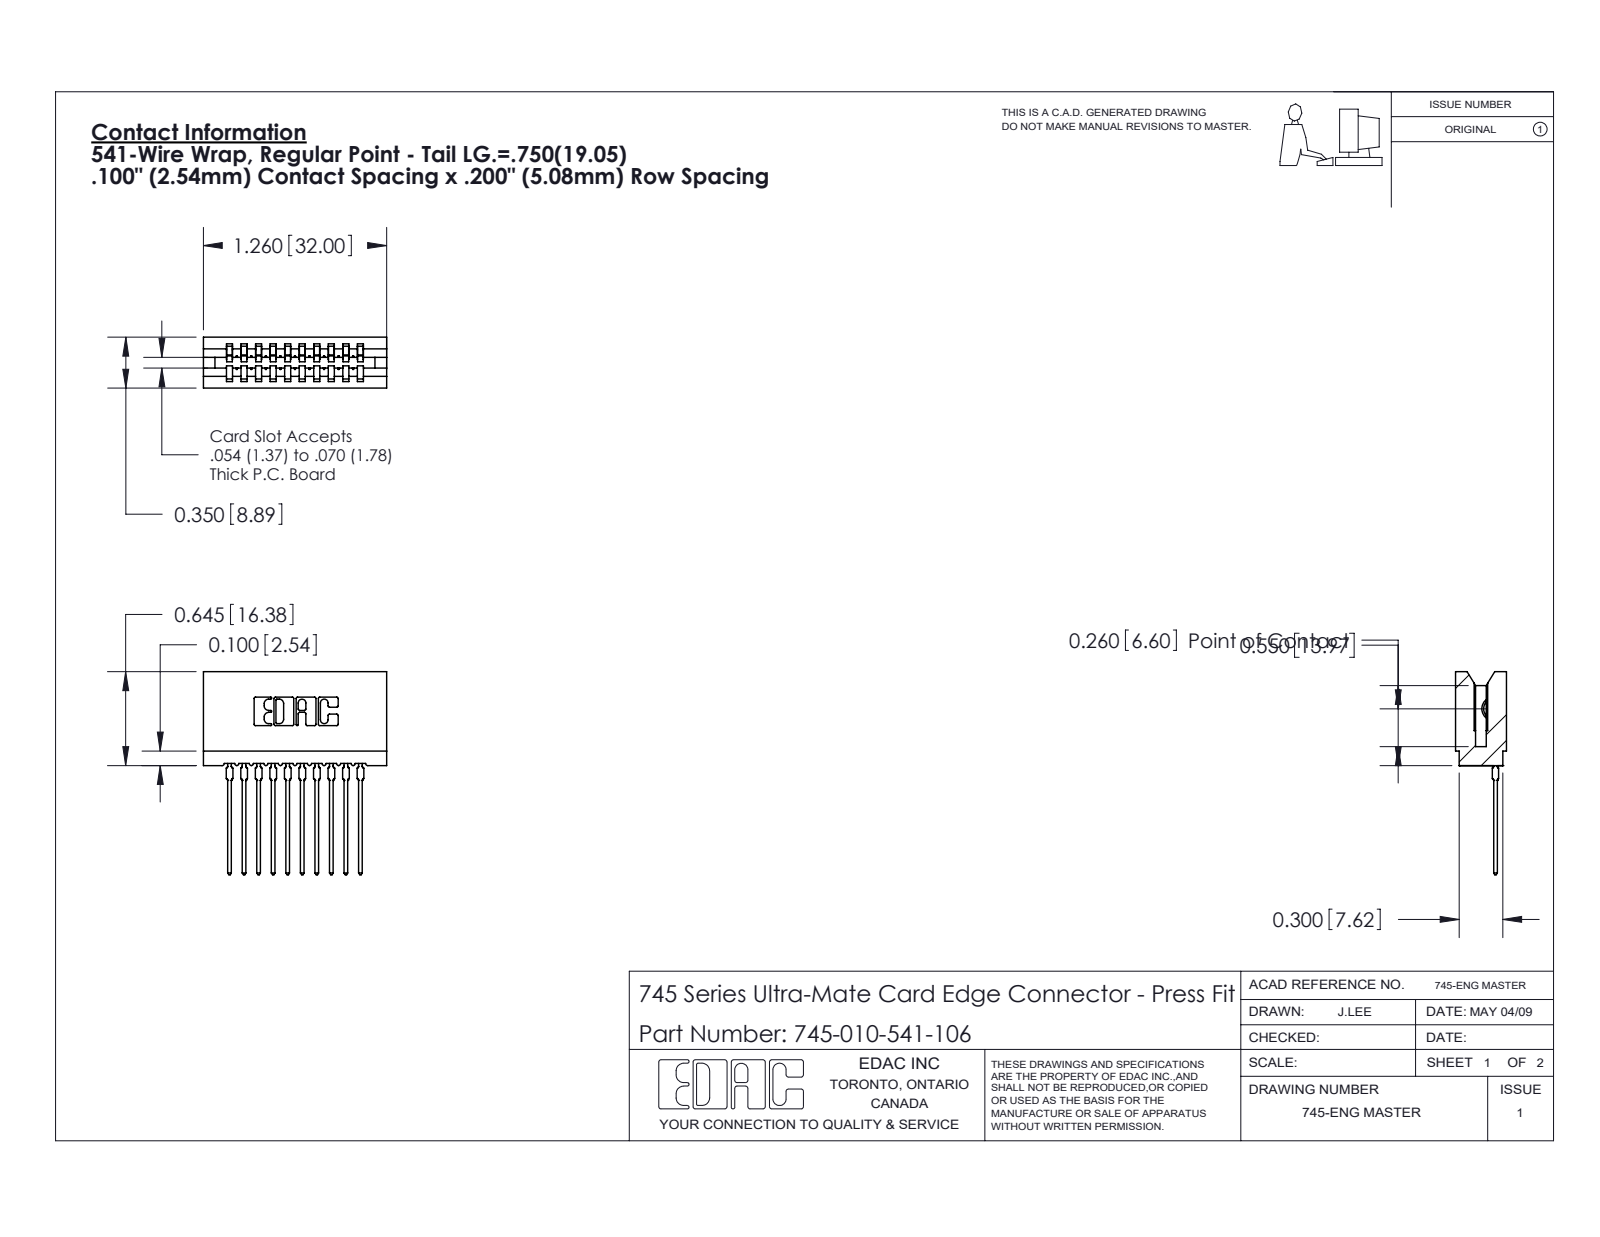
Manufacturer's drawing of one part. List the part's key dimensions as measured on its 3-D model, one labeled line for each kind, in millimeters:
Part name (STEP PRODUCT): 745-292-001_541; 745-010-541-106; 745 Part_Insulator Option - 06
STEP written by: SolidWorks 2020 (CONFIG_CONTROL_DESIGN)
Units: millimetres
Bodies: 11 solids, 1216 faces (726 planar, 230 cylindrical, 260 other)
Overall size (bounding box): 35.5 × 32 × 8.9
Volume: 3 000 mm³ · Surface area: 5 186 mm²
Partial cylindrical surfaces — rounded edges, fillets, slot ends (radius × count): R0.3 ×22, R0.4 ×20, R0.5 ×20, R0.2 ×6, R0.8 ×6, R0.1 ×4, R0.3 ×4, R0.7 ×3
Main face-to-face distances: 2.5, 5.1, 7.6, 10.2, 1.1, 3.6, 12.7, 1.5, 6.1, 4
